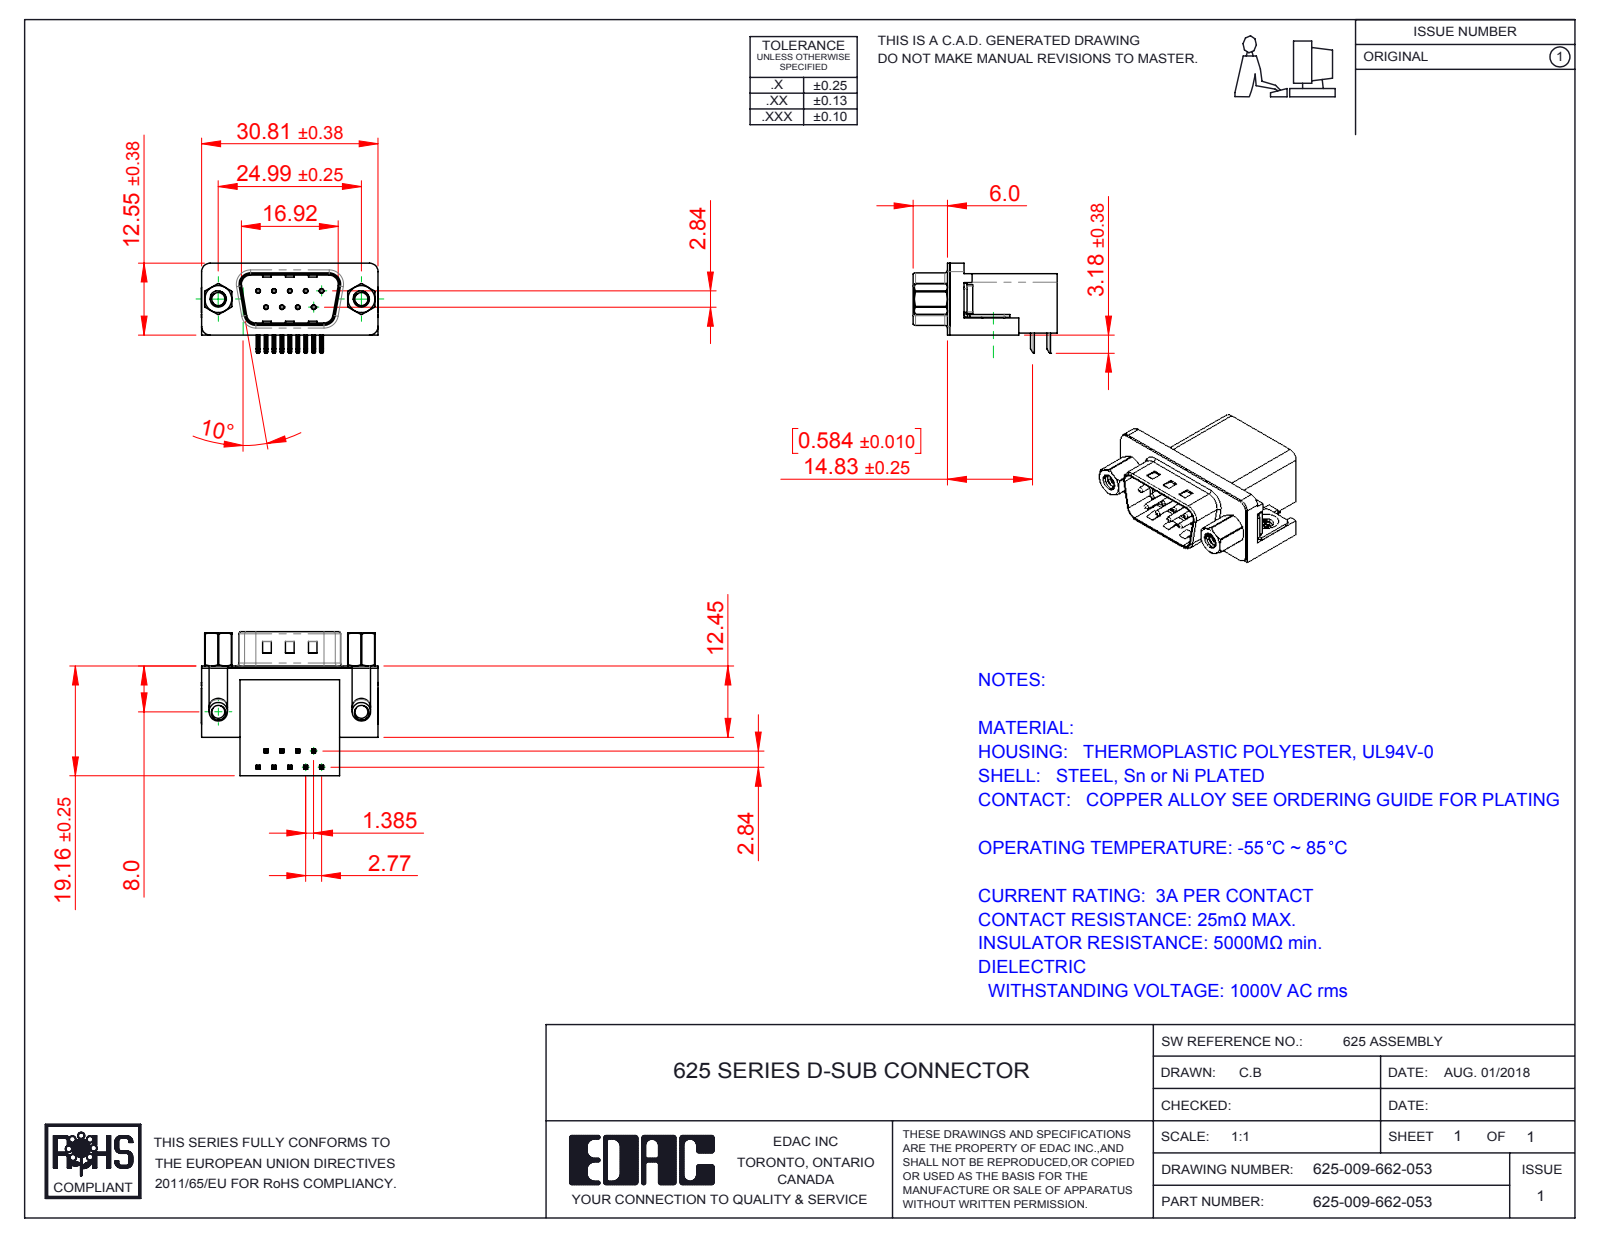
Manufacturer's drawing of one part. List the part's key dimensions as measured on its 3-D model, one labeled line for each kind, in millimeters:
Part name (STEP PRODUCT): 625 Contact Bottom; 625 4-40 Threaded Rivet; 625 Contact Top; 625 Shell_9 Socket (+4 more)
STEP written by: SolidWorks 2016 (CONFIG_CONTROL_DESIGN)
Units: millimetres
Bodies: 17 solids, 1151 faces (597 planar, 401 cylindrical, 153 other)
Overall size (bounding box): 30.89 × 25.16 × 15.73
Volume: 4 700 mm³ · Surface area: 5 514 mm²
Round holes (diameter × count): ⌀0.35 ×9, ⌀0.8 ×9, ⌀2.26 ×4, ⌀2.29 ×2, ⌀4 ×2, ⌀4.8 ×2, ⌀5 ×2
Round bosses / shafts (diameter × count): ⌀0.75 ×9, ⌀4.9 ×2, ⌀4.75 ×2, ⌀3.9 ×2, ⌀3.26 ×2, ⌀2.79 ×2
Partial cylindrical surfaces — rounded edges, fillets, slot ends (radius × count): R0.25 ×44, R0.12 ×18, R1 ×16, R0.5 ×9, R1.5 ×8, R1.6 ×8, R0.9 ×4, R2 ×4
Main face-to-face distances: 0.4, 10.34, 18.76, 19.16, 16.26, 2.5, 2.9, 0.35, 10.69, 6.7
Hole centre spacings: 3.16, 2.77, 5.54, 5.03, 5.04, 8.31, 7.48, 7.49
